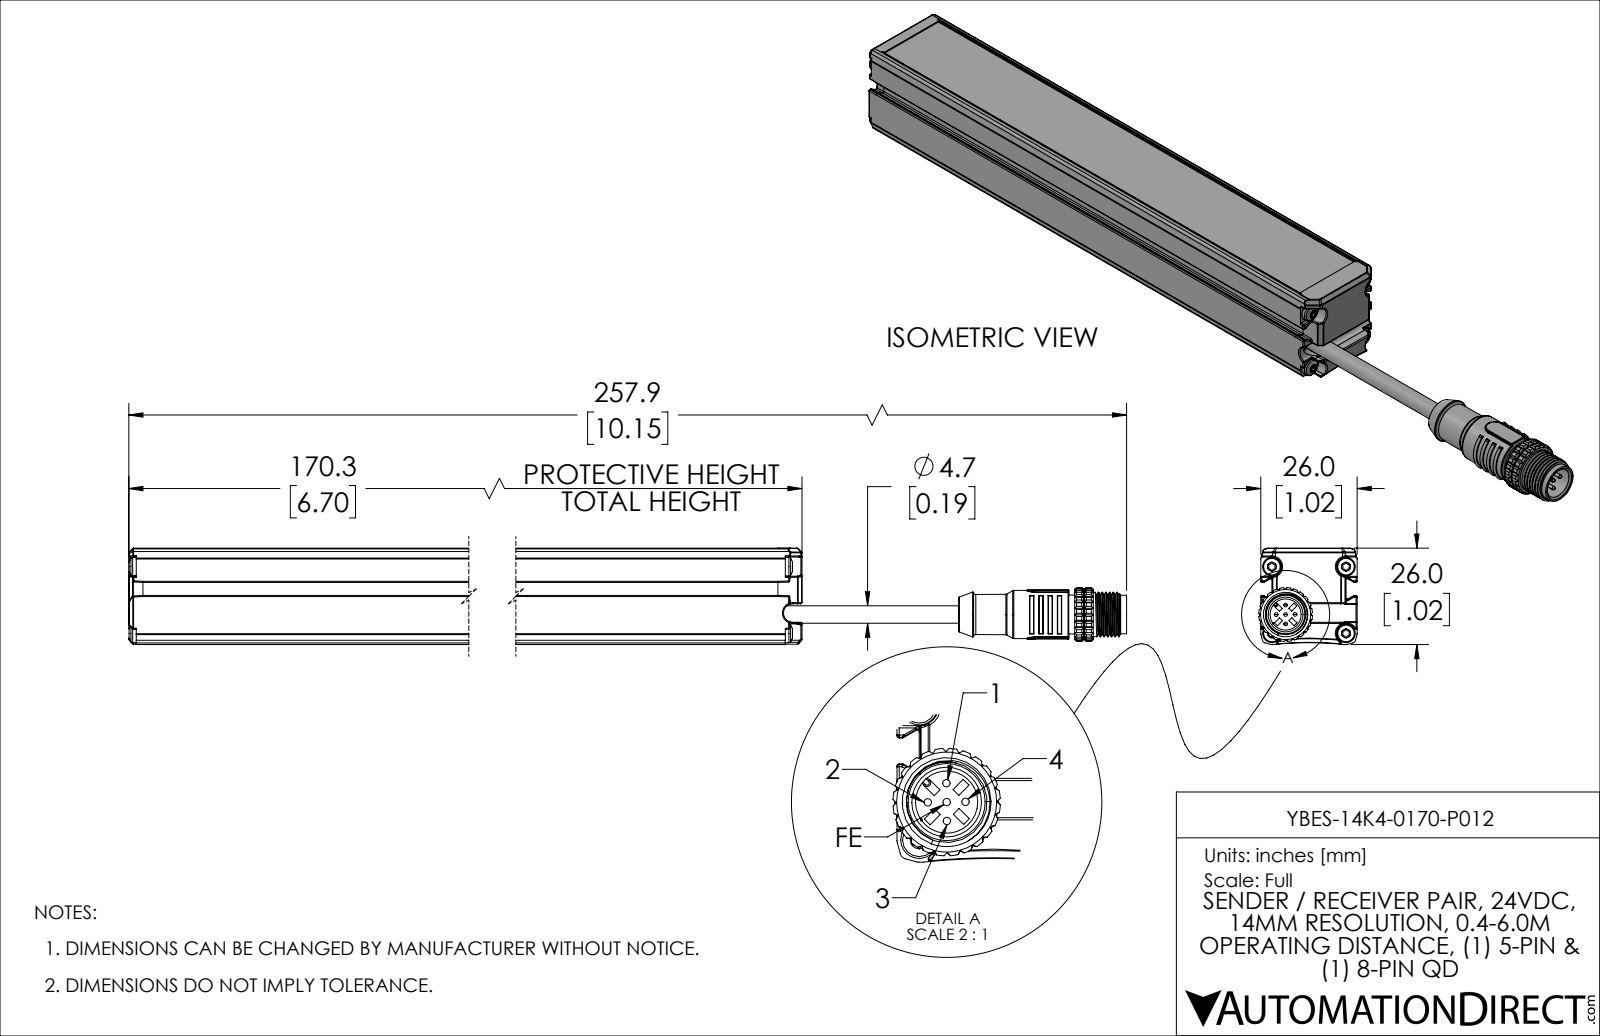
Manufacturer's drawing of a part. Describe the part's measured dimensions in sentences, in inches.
The part is named "YBES-14K4-0170-P012_REV1". Its 3-D file was written by "SolidWorks 2019 (AUTOMOTIVE_DESIGN)". It is 2 solids with 1738 faces: 544 planar, 719 cylindrical and 475 other. Overall it measures 10.154 by 1.045 by 1.024 inches. Its volume is 2.813 cubic inches and its surface area 75.63 square inches. Round holes: 4 of diameter 0.094, 4 of diameter 0.1, 4 of diameter 0.146, 4 of diameter 0.197, 1 of diameter 0.189, 1 of diameter 0.232, 1 of diameter 0.331. Round bosses or shafts: 5 of diameter 0.039, 4 of diameter 0.126, 4 of diameter 0.098, 4 of diameter 0.051, 2 of diameter 0.059, 1 of diameter 0.531, 1 of diameter 0.512, 1 of diameter 0.472. Partial cylindrical surfaces (rounded edges, fillets, slot ends): 153 of radius 0.008, 115 of radius 0.012, 24 of radius 0.008, 24 of radius 0.015, 18 of radius 0.039, 16 of radius 0.016, 10 of radius 0.006, 7 of radius 0.02. The main face-to-face distances are 0.118, 0.059, 0.071, 0.835, 1.024, 0.717, 0.047, 0.016, 0.906, 0.787. The hole center spacings are 0.709, 0.787, 1.059, 0.248, 0.528, 0.672, 0.819.
